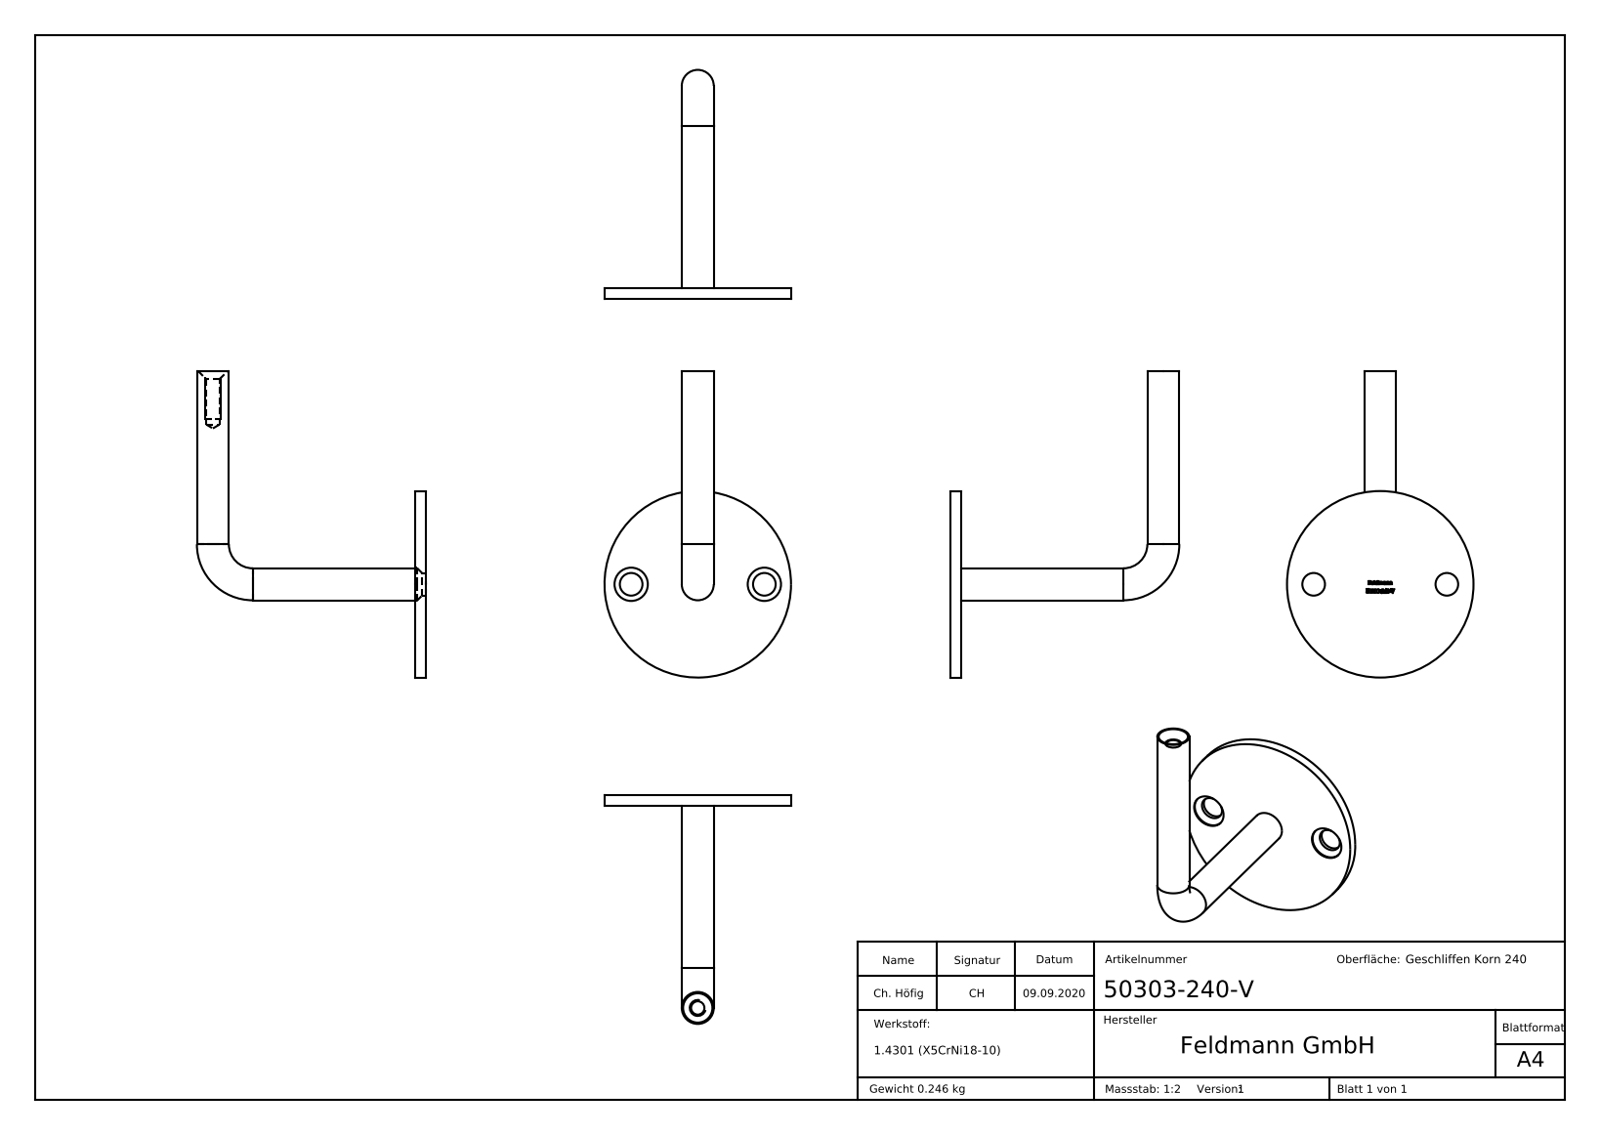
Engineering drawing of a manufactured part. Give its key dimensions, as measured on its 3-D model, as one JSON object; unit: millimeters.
{"part_name": "50303-240-V", "step_written_by": "SolidWorks 2018 (CONFIG_CONTROL_DESIGN)", "units": "millimeters", "bodies": {"solids": 1, "faces": 272, "planar": 129, "cylindrical": 16, "other": 127}, "overall_size": [115, 86, 70], "volume_mm3": 31163, "surface_area_mm2": 14474, "round_holes": [[8.5, 2], [12.5, 2], [5, 1]], "round_bosses_or_shafts": [[12, 2], [70, 1]], "face_to_face_distances": [4, 3.9, 2.97, 0.39, 3.09, 4.09, 1.32, 1.12, 3.66, 6.36], "hole_center_spacings": [50]}
